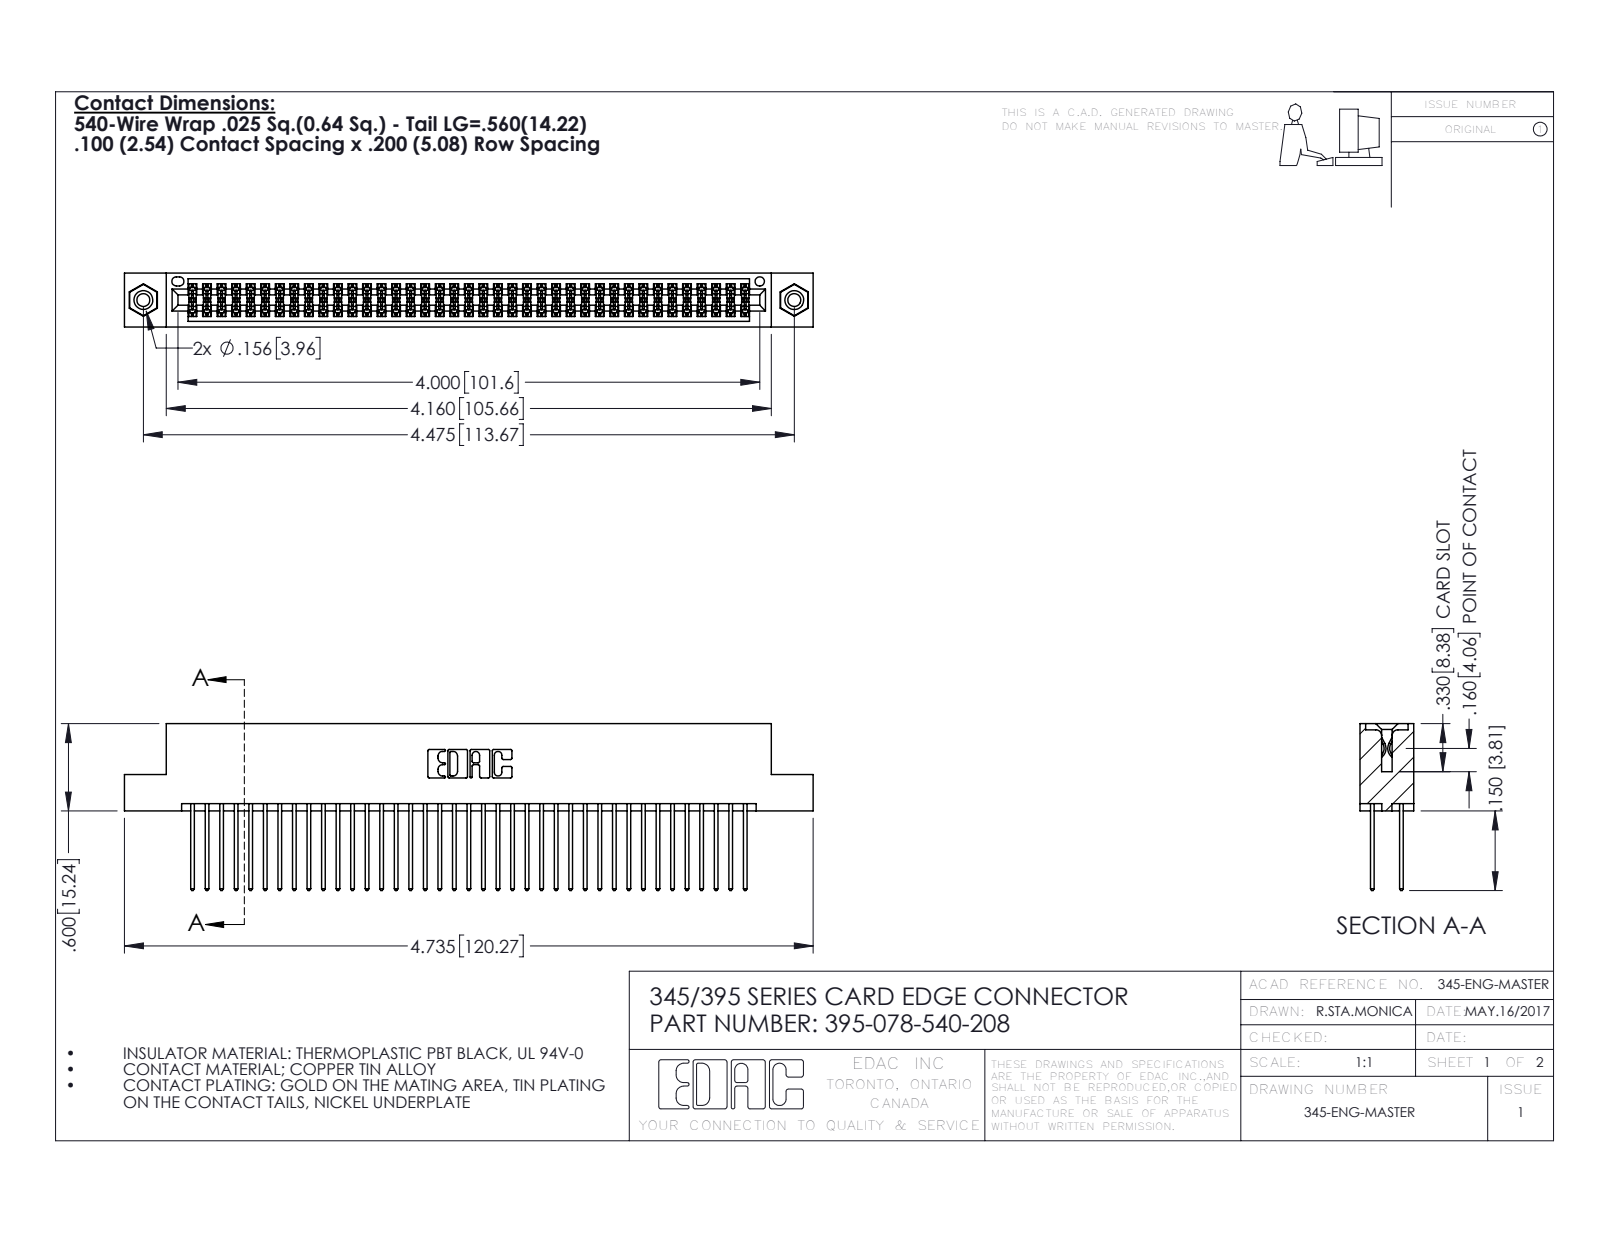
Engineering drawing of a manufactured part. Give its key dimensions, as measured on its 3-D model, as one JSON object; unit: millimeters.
{"part_name": "345 Part_Flush Mounting Lugs - 0.156 Dia-TI; 345-250-001_345-250-003-102; 395-078-540-208; 345-292-001_345-293-140", "step_written_by": "SolidWorks 2016 (CONFIG_CONTROL_DESIGN)", "units": "millimeters", "bodies": {"solids": 81, "faces": 4086, "planar": 2686, "cylindrical": 1384, "other": 16}, "overall_size": [120.3, 29.1, 9.4], "volume_mm3": 11900, "surface_area_mm2": 18980, "round_holes": [[2.3, 2], [3.2, 2], [4, 2], [1.6, 1]], "round_bosses_or_shafts": [[3.9, 2]], "partial_cylinders_radius": [[0.2, 117], [0.3, 78], [0.3, 22], [0.2, 6], [0.8, 6], [0.7, 3], [0.4, 2], [0.5, 2]], "face_to_face_distances": [1.8, 7.6, 5.1, 2.5, 6.9, 0.6, 9.4, 5.7, 4.4, 3.8], "hole_center_spacings": [6.9, 107.7, 113.7]}
